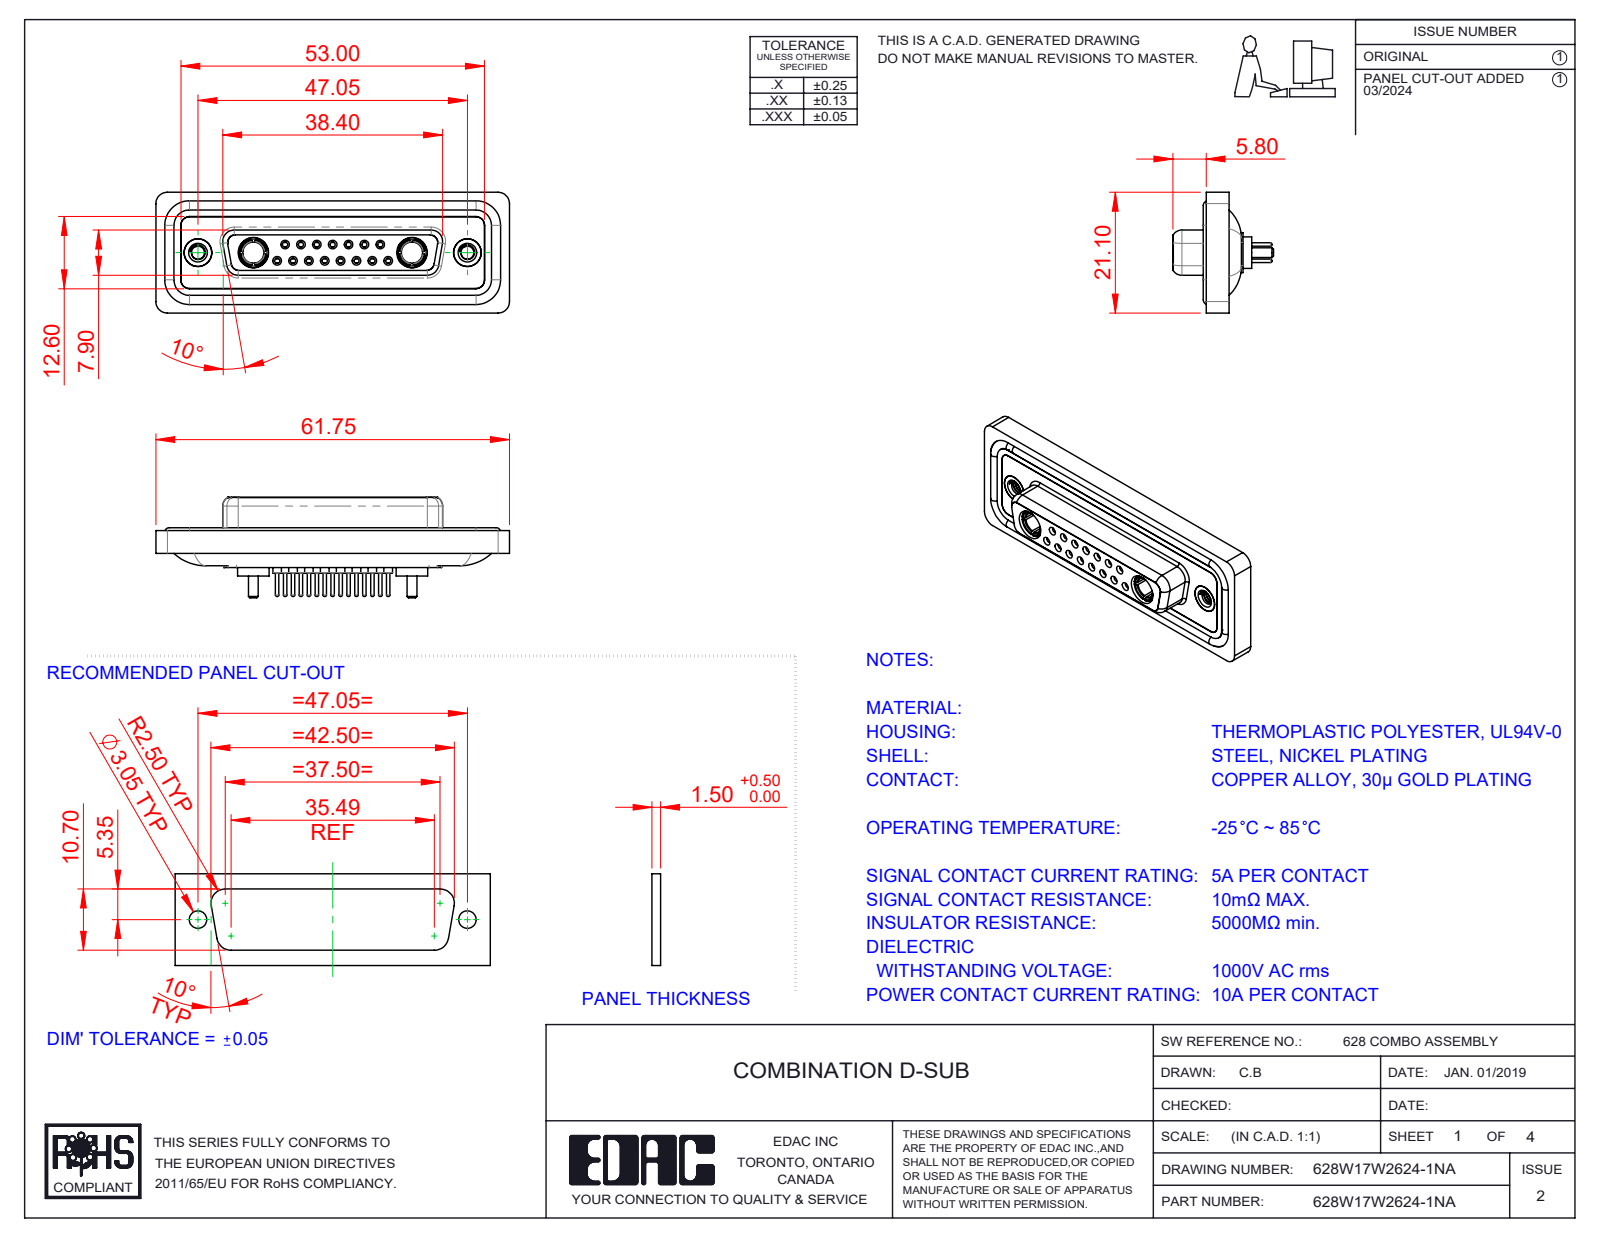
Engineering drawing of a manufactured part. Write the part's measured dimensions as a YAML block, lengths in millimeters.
part_name: "628Combo Housing_17W2; 628Combo Threaded Rivet_A; 628W17W2624-1NA; 628Combo Waterproof Housing_25 Contacts (+5 more)"
step_written_by: "SolidWorks 2023 (CONFIG_CONTROL_DESIGN)"
units: millimeters
bodies: {solids: 26, faces: 1357, planar: 388, cylindrical: 521, other: 448}
overall_size: [61.75, 21.1, 17.55]
volume: 8296
surface_area: 13828
round_holes:
  - {diameter: 0.9, count: 15}
  - {diameter: 1.1, count: 15}
  - {diameter: 1.5, count: 15}
  - {diameter: 2, count: 15}
  - {diameter: 1.6, count: 8}
  - {diameter: 1.7, count: 7}
  - {diameter: 4.85, count: 4}
  - {diameter: 2.26, count: 2}
  - {diameter: 3.7, count: 2}
  - {diameter: 4, count: 2}
  - {diameter: 4.05, count: 2}
  - {diameter: 5, count: 2}
round_bosses_or_shafts:
  - {diameter: 2.2, count: 15}
  - {diameter: 0.6, count: 15}
  - {diameter: 1.6, count: 11}
  - {diameter: 5.5, count: 2}
  - {diameter: 5.2, count: 2}
  - {diameter: 4.96, count: 2}
  - {diameter: 4.95, count: 2}
  - {diameter: 4.8, count: 2}
partial_cylinders:
  - {radius: 1.5, count: 22}
  - {radius: 2, count: 18}
  - {radius: 1.35, count: 8}
  - {radius: 1.6, count: 8}
  - {radius: 0.25, count: 4}
  - {radius: 0.5, count: 4}
  - {radius: 0.6, count: 4}
  - {radius: 0.65, count: 4}
face_to_face_distances: [0.4, 1.8, 7.45, 5.65, 6.6, 0.5, 7.05, 1.6, 2.9, 1.1]
hole_center_spacings: [3.16, 2.77, 8.31, 5.54, 5.03, 5.04, 7.49, 11.08]
